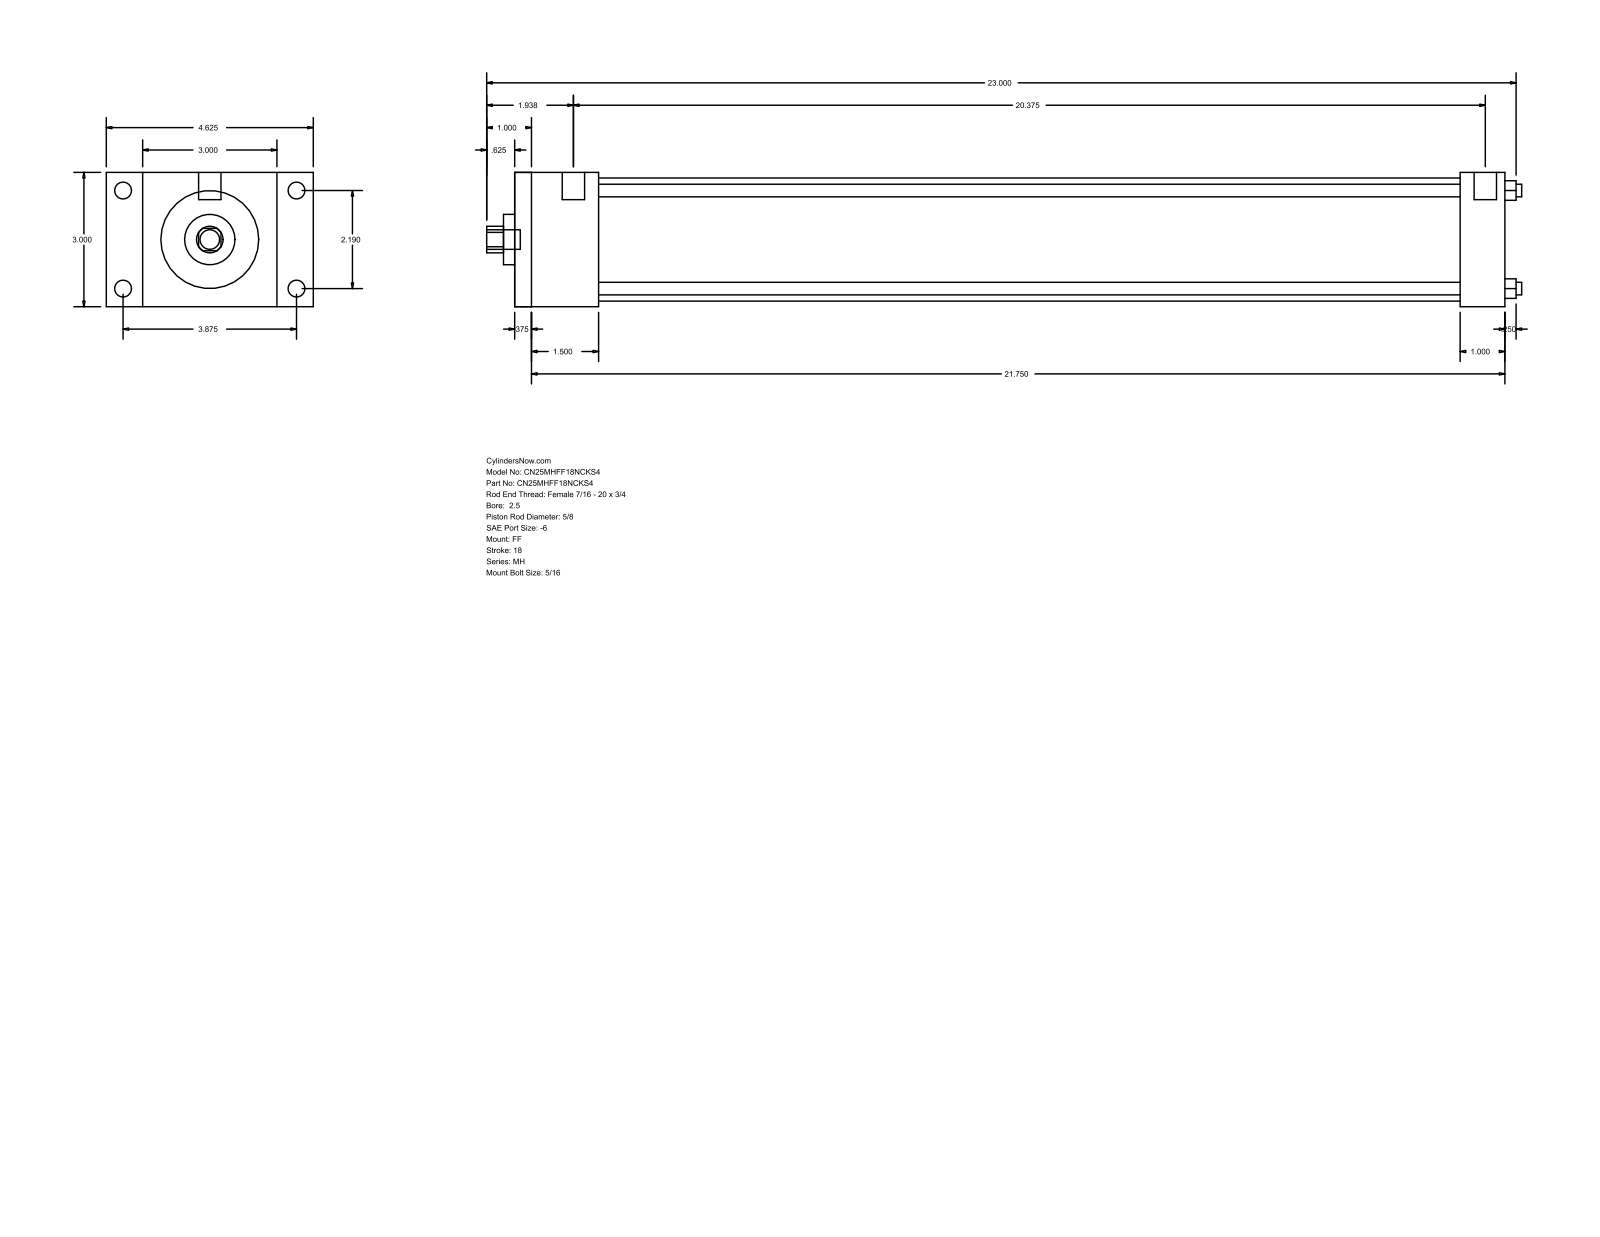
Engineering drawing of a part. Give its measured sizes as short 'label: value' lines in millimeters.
name: MH_FF__0250_0.625
written by: GSSL Pune (CONFIG_CONTROL_DESIGN)
unit: mm
bodies: 0 solids, 92 faces (64 planar, 28 cylindrical, 0 other)
size: 587.38 × 117.47 × 76.2
holes: 4× ⌀7.14, 1× ⌀15.88, 1× ⌀28.57, 1× ⌀69.85
bosses: 4× ⌀9.53, 4× ⌀5.56, 2× ⌀12.7, 1× ⌀11.11
rounds: 1× R7.54
face distances: 76.2, 561.97, 9.52, 552.45, 25.4, 47.62, 536.57, 38.1, 527.05, 488.95
hole spacings: 39.33, 55.62, 78.66
